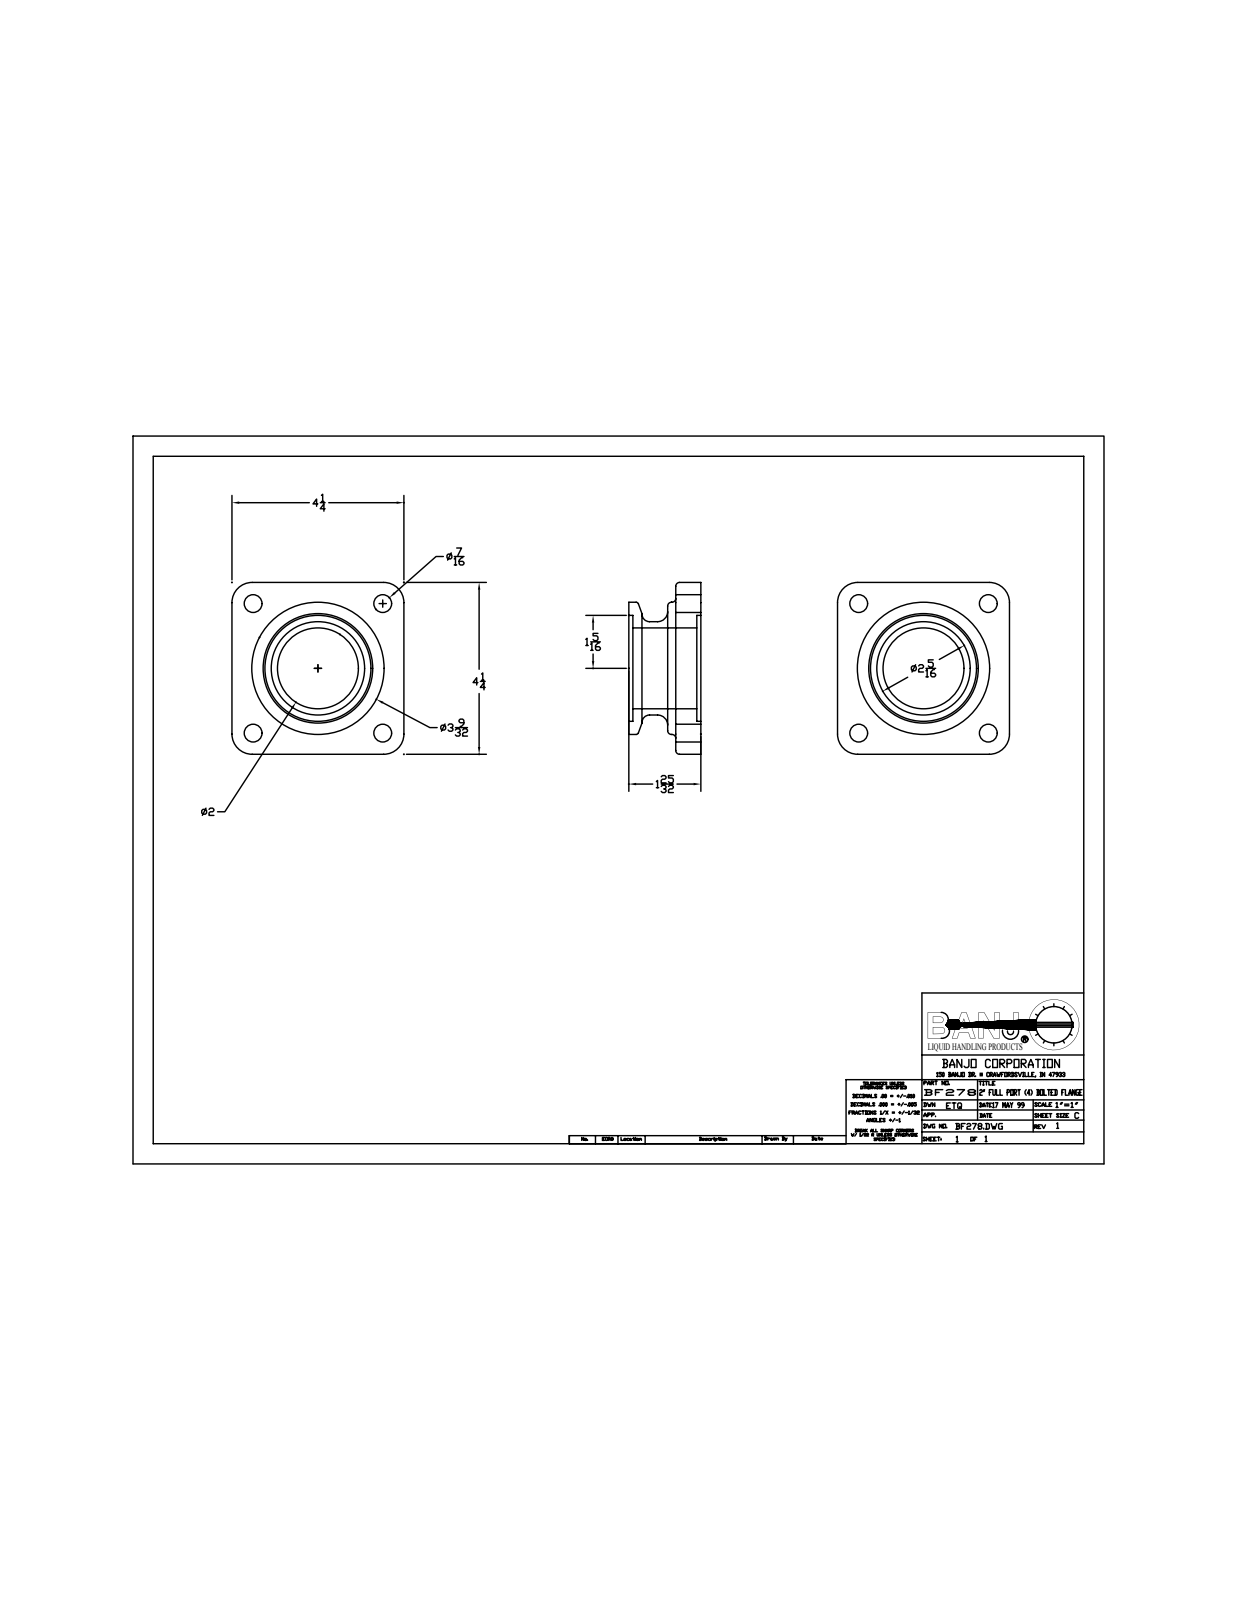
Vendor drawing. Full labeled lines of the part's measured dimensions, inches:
Part name (STEP PRODUCT): BF278
STEP written by: Mechanical Desktop 2009 (CONFIG_CONTROL_DESIGN)
Units: inches
Bodies: 1 solid, 55 faces (11 planar, 28 cylindrical, 16 other)
Overall size (bounding box): 4.25 × 4.25 × 1.78
Volume: 11.7 in³ · Surface area: 67.84 in²
Round holes (diameter × count): ⌀0.44 ×4, ⌀2 ×1, ⌀2.62 ×1
Round bosses / shafts (diameter × count): ⌀3.27 ×1, ⌀2.308 ×1
Partial cylindrical surfaces — rounded edges, fillets, slot ends (radius × count): R0.094 ×4, R0.5 ×4
Main face-to-face distances: 0.62, 0.1, 1.68, 4.25, 1.78, 1.16, 1.06, 0.52, 1.58, 0.82
Hole centre spacings: 2.265, 3.203, 4.53
